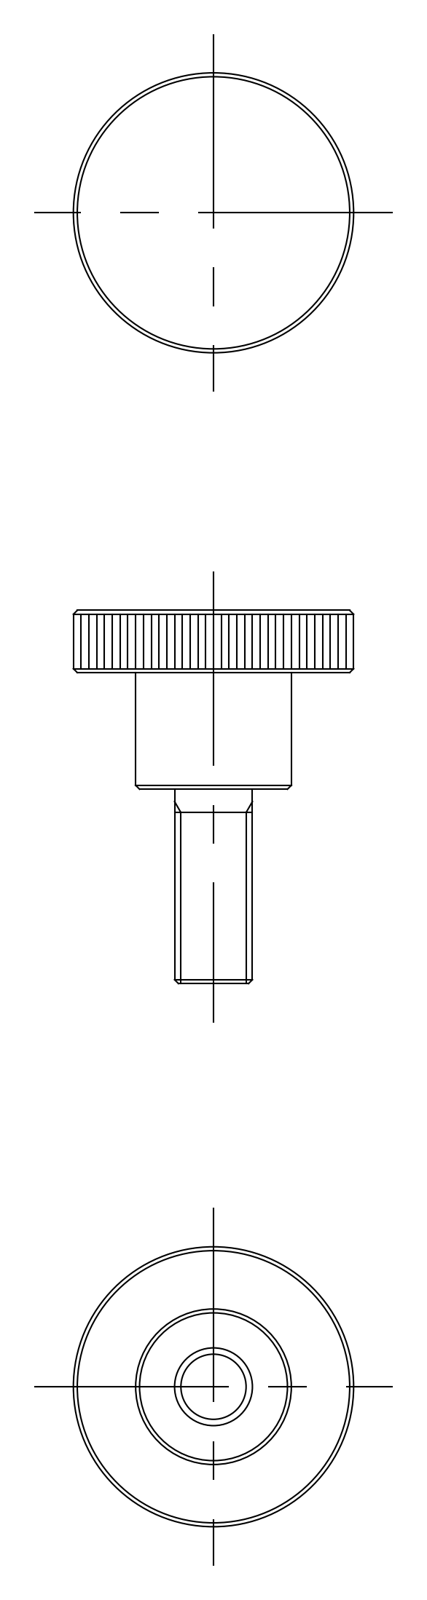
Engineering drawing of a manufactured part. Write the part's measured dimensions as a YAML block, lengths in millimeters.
part_name: "knob"
step_written_by: "CADfix (AUTOMOTIVE_DESIGN)"
units: millimeters
bodies: {solids: 1, faces: 18, planar: 0, cylindrical: 0, other: 18}
overall_size: [48, 36, 36]
volume: 14806
surface_area: 4574
